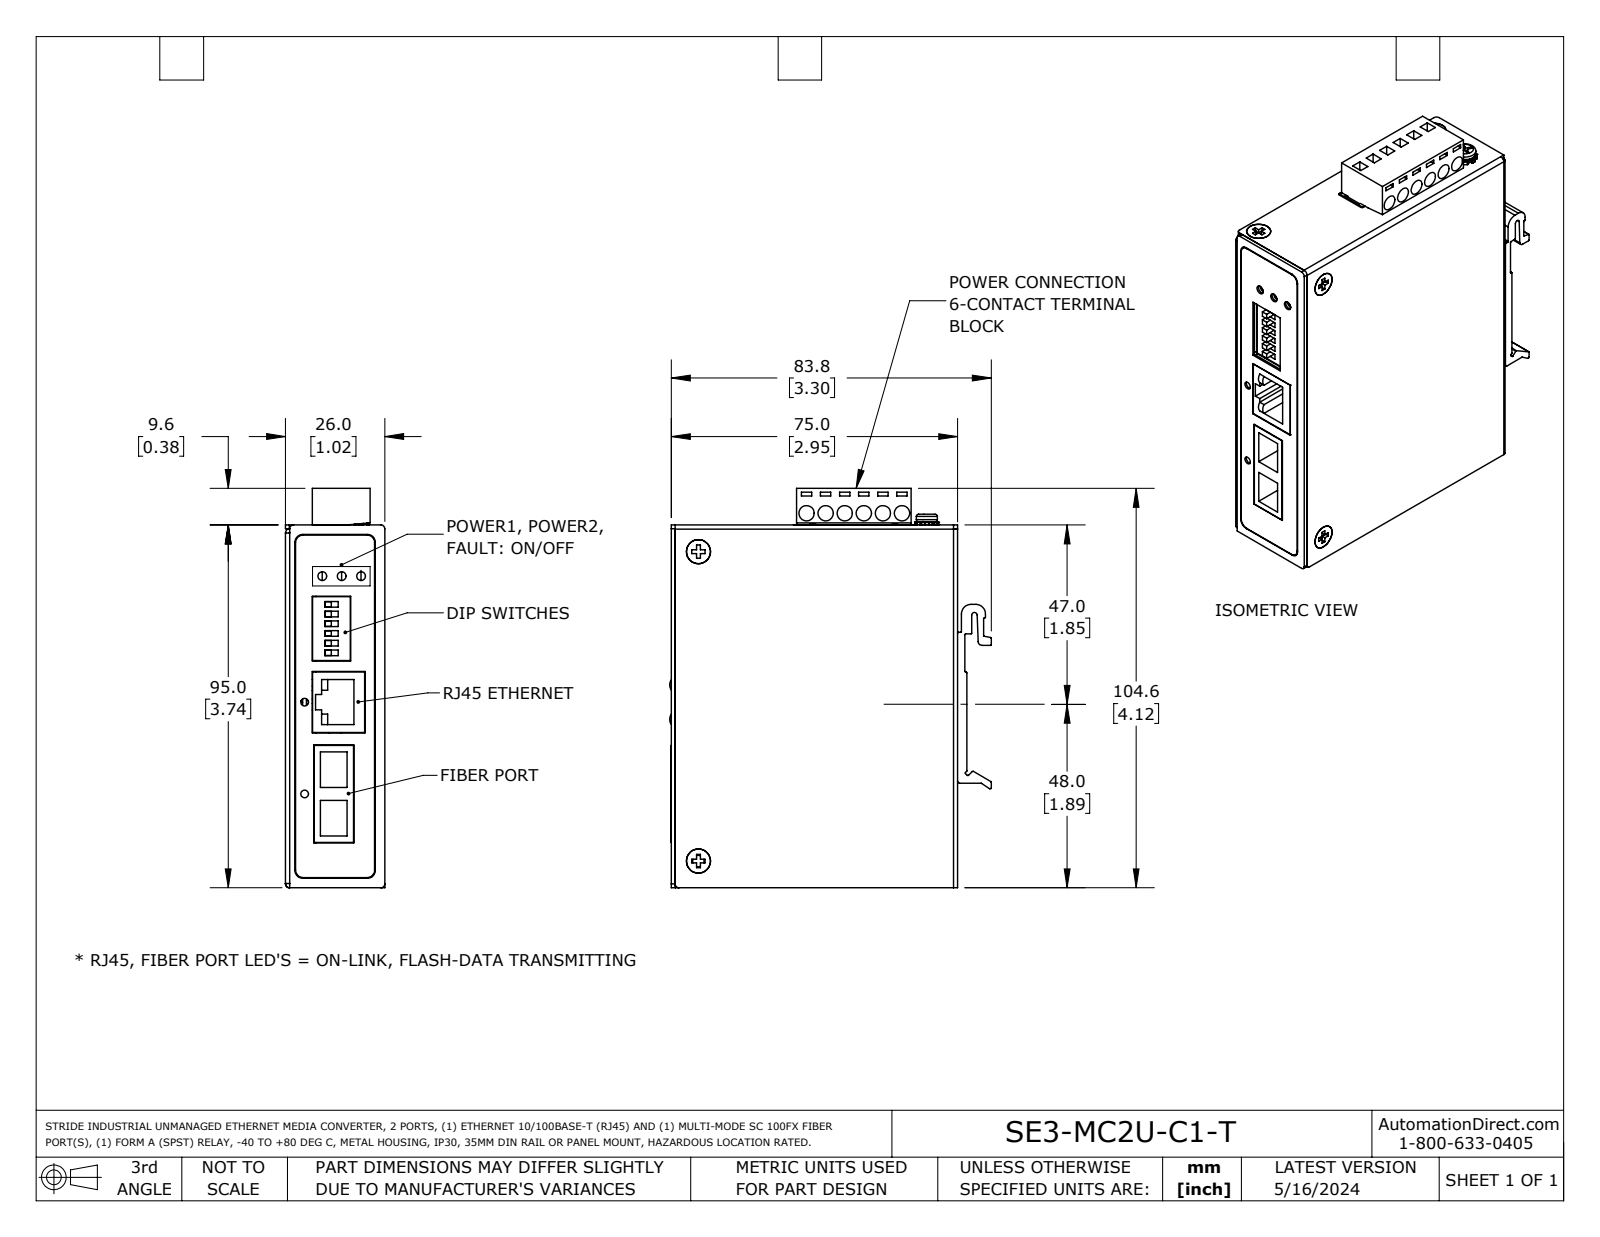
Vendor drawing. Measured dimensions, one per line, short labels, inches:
name: SE3-MC2U-C1-T
written by: SolidWorks 2023 (AUTOMOTIVE_DESIGN)
unit: in
bodies: 21 solids, 1013 faces (629 planar, 272 cylindrical, 112 other)
size: 4.116 × 3.316 × 1.024
volume: 2.937 in³; area: 105.8 in²
holes: 23× ⌀0.118, 9× ⌀0.157, 3× ⌀0.091, 3× ⌀0.126, 2× ⌀0.079, 2× ⌀0.087, 2× ⌀0.114, 1× ⌀0.059
bosses: 16× ⌀0.197, 6× ⌀0.039, 6× ⌀0.02, 4× ⌀0.118, 1× ⌀0.217
rounds: 59× R0.004, 25× R0.02, 18× R0.039, 17× R0.008, 8× R0.079, 7× R0.043, 6× R0.118, 4× R0.138
face distances: 0.039, 0.02, 0.984, 0.965, 0.059, 0.945, 1.024, 2.894, 3.701, 1.004
hole spacings: 0.197, 0.394, 0.591, 0.406, 0.787, 2.953, 0.2, 0.419
